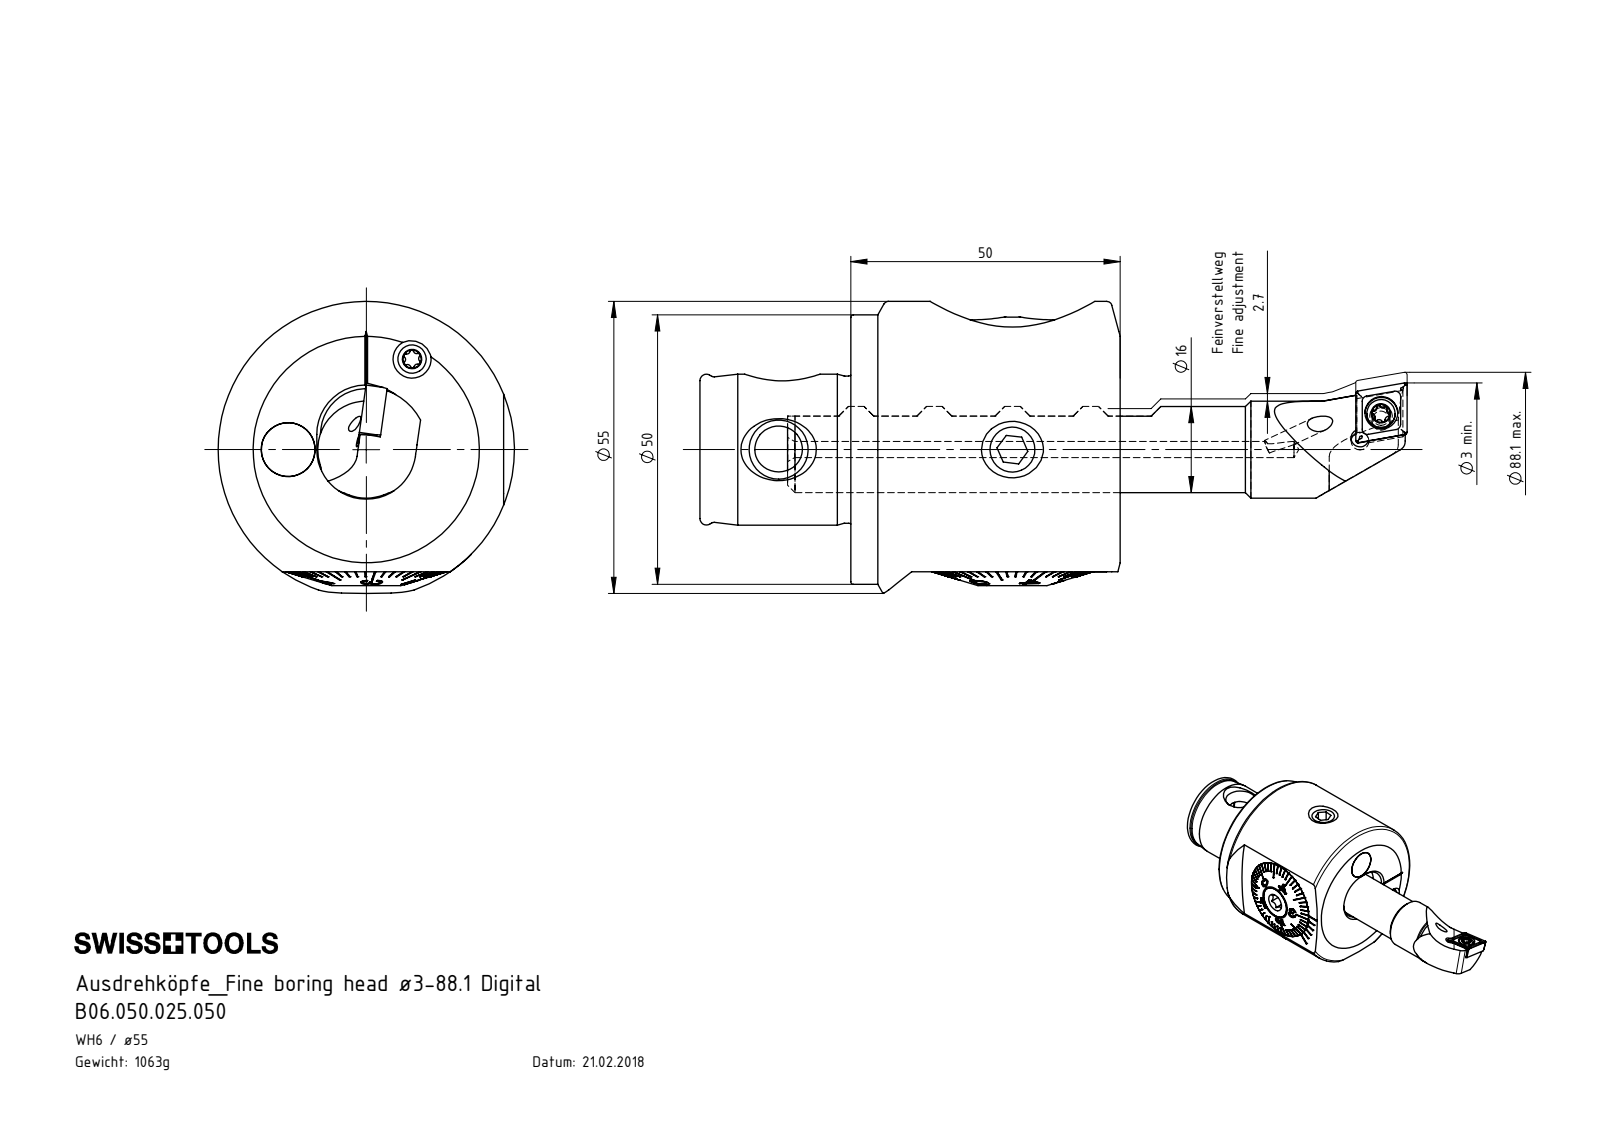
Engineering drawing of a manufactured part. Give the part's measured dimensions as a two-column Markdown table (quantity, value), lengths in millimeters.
| quantity | value |
| --- | --- |
| part name | ISO 4026 - M10 x 8; Fxx-MAB.xxx.xxx_A_F32x1.3; DIN 3771 - 25x1.5; WH5-A55.DA1.050_A (+8 more) |
| STEP written by | SolidWorks 2017 (CONFIG_CONTROL_DESIGN) |
| units | millimeters |
| bodies | 27 solids, 1146 faces (470 planar, 291 cylindrical, 385 other) |
| overall size | 131.25 × 55 × 54.18 |
| volume | 124 590 mm³ |
| surface area | 49 997 mm² |
| round holes (diameter × count) | 3.2 × 4, 1.6 × 3, 3.3 × 3, 4.2 × 3, 8.5 × 3, 2.2 × 2, 3 × 2, 4.4 × 1, 6.1 × 1, 8 × 1, 10 × 1, 10.1 × 1 |
| round bosses / shafts (diameter × count) | 1.9 × 6, 10 × 3, 18 × 2, 5.25 × 2, 4 × 2, 3.8 × 2, 2 × 2, 55 × 1 |
| partial cylindrical surfaces (radius × count) | 0.34 × 12, 0.59 × 12, 1.2 × 8, 1.1 × 6, 4.5 × 4, 3.2 × 3, 4.4 × 3, 3.1 × 2 |
| main face-to-face distances | 50, 3.7, 2, 4, 2.8, 5.3, 1.2, 5.65, 22, 27.65 |
| hole center spacings | 4.1, 4.32, 7.25, 8.45, 9.52, 12, 12.68, 14.5 |
